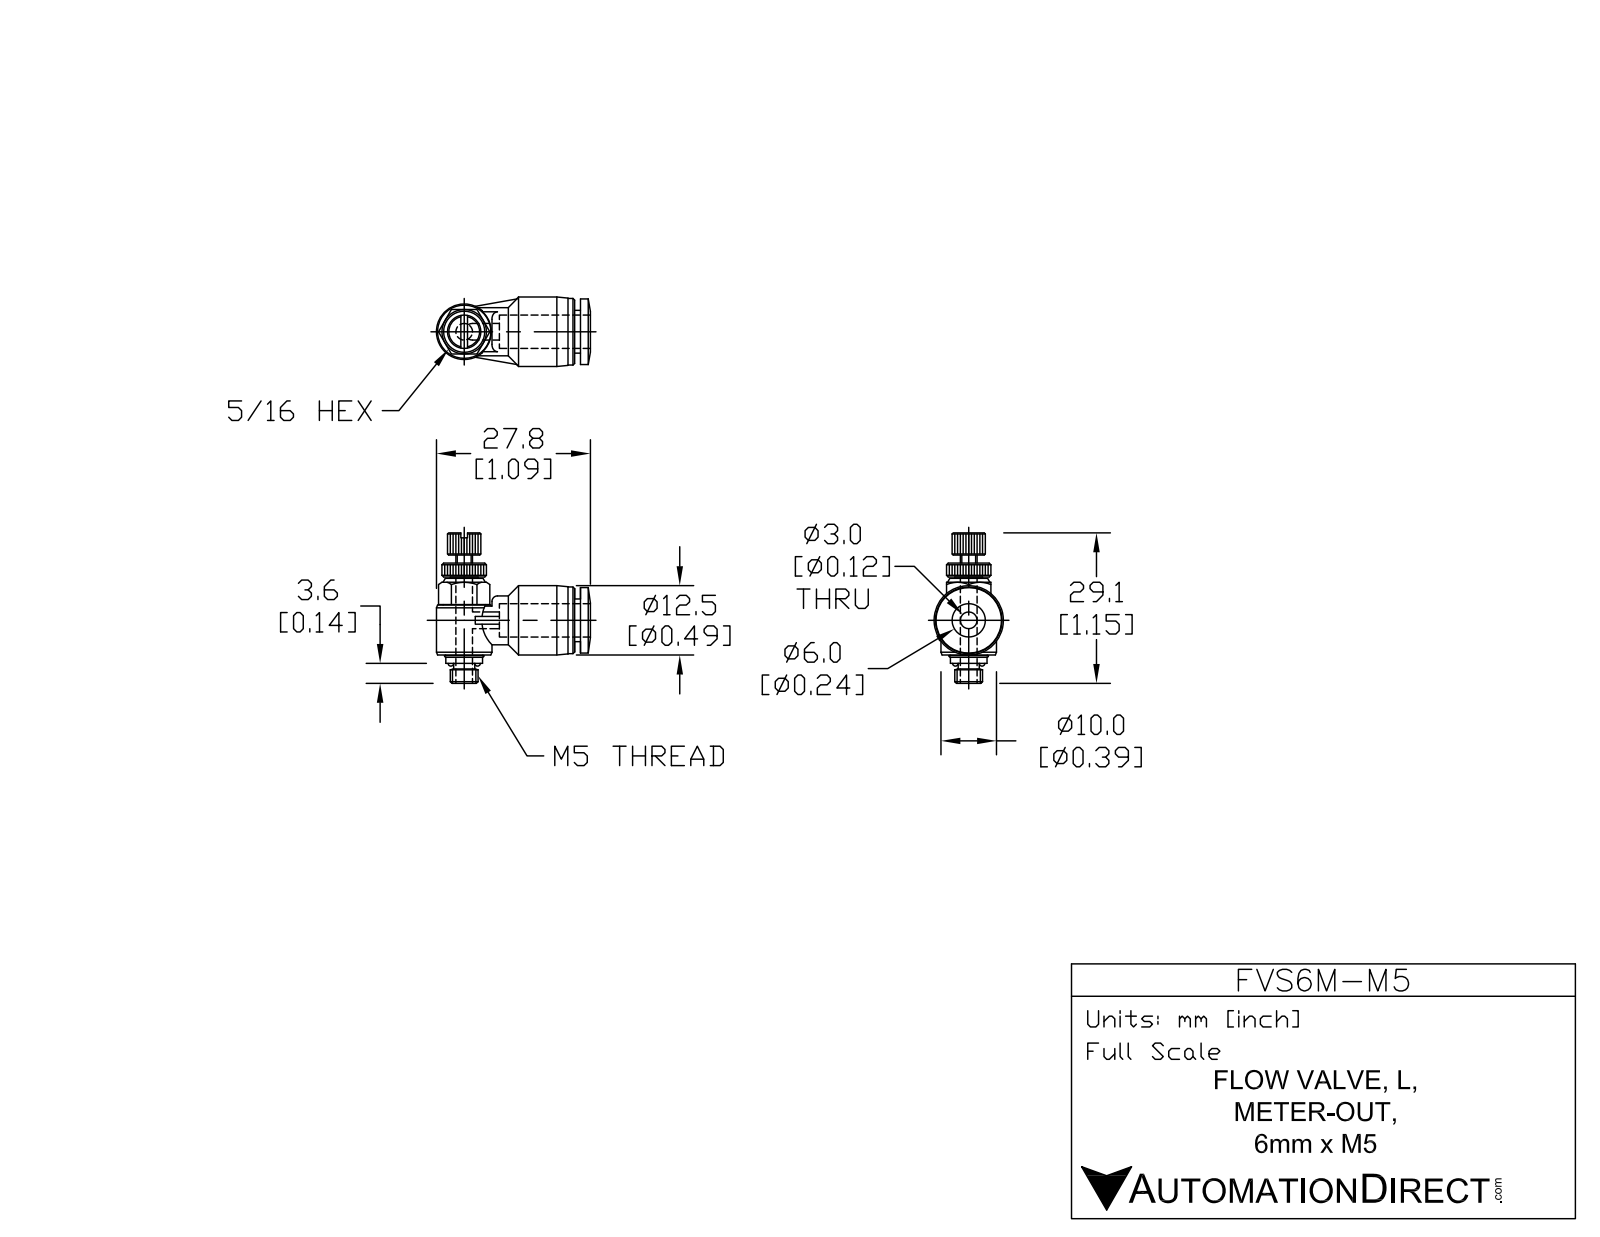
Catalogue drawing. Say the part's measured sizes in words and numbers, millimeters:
The part is named "FVS6M-M5". Its 3-D file was written by "SolidWorks 2015 (AUTOMOTIVE_DESIGN)". It is 2 solids with 345 faces: 152 planar, 97 cylindrical and 96 other. Overall it measures 29.1 by 27.8 by 12.5 millimeters. Its volume is 2 610 cubic millimeters and its surface area 2 333 square millimeters. Round holes: 2 of diameter 2, 1 of diameter 3.8, 1 of diameter 6.3. Round bosses or shafts: 1 of diameter 12.5, 1 of diameter 12, 1 of diameter 11.8, 1 of diameter 10, 1 of diameter 8.8, 1 of diameter 7.7, 1 of diameter 7.6, 1 of diameter 7.1. Partial cylindrical surfaces (rounded edges, fillets, slot ends): 1 of radius 3, 1 of radius 4. The main face-to-face distances are 1, 8, 16.6, 3.5, 14.6, 7.5, 4, 5.2, 11, 13.5.
